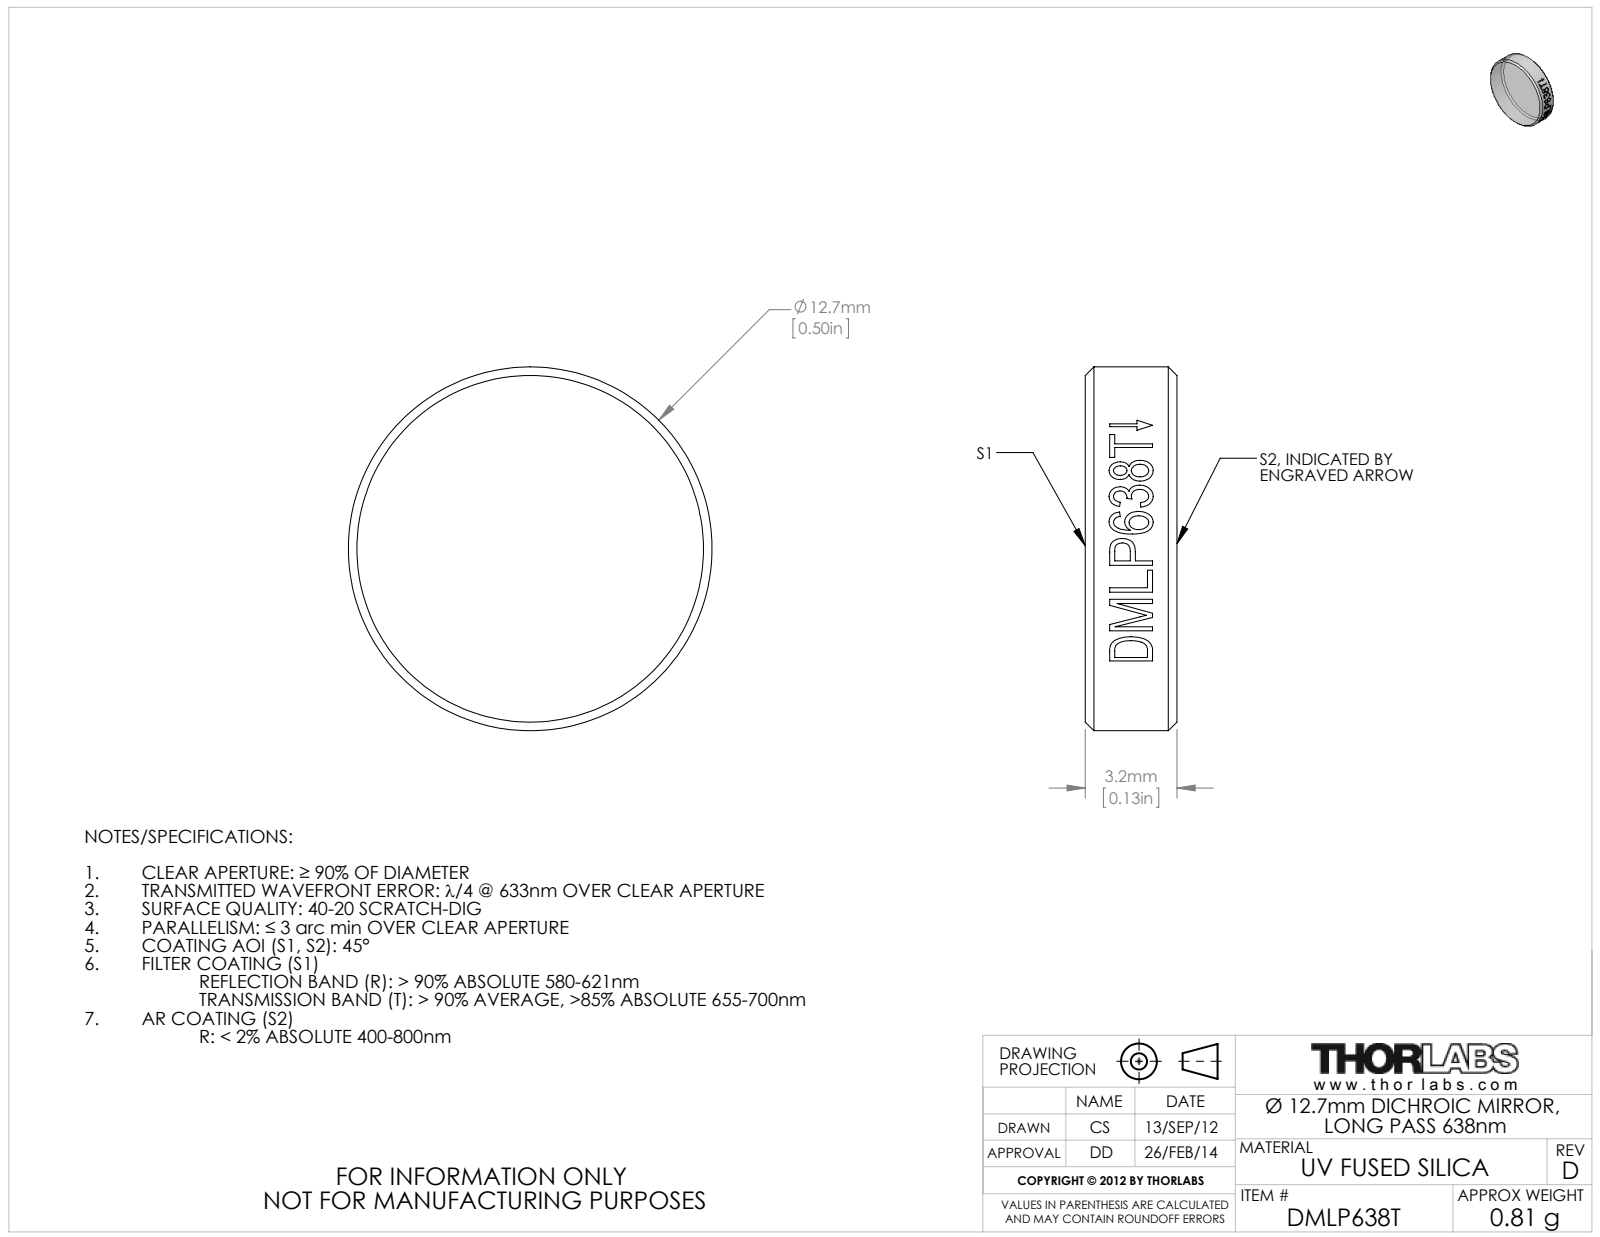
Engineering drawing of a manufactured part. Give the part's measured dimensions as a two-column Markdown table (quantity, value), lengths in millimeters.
| quantity | value |
| --- | --- |
| part name | 24965-E0W |
| STEP written by | SolidWorks 2011 (CONFIG_CONTROL_DESIGN) |
| units | millimeters |
| bodies | 0 solids, 22 faces (2 planar, 16 cylindrical, 4 other) |
| overall size | 12.7 × 12.7 × 3.2 |
| round bosses / shafts (diameter × count) | 12.7 × 1 |
| main face-to-face distances | 3.2 |
